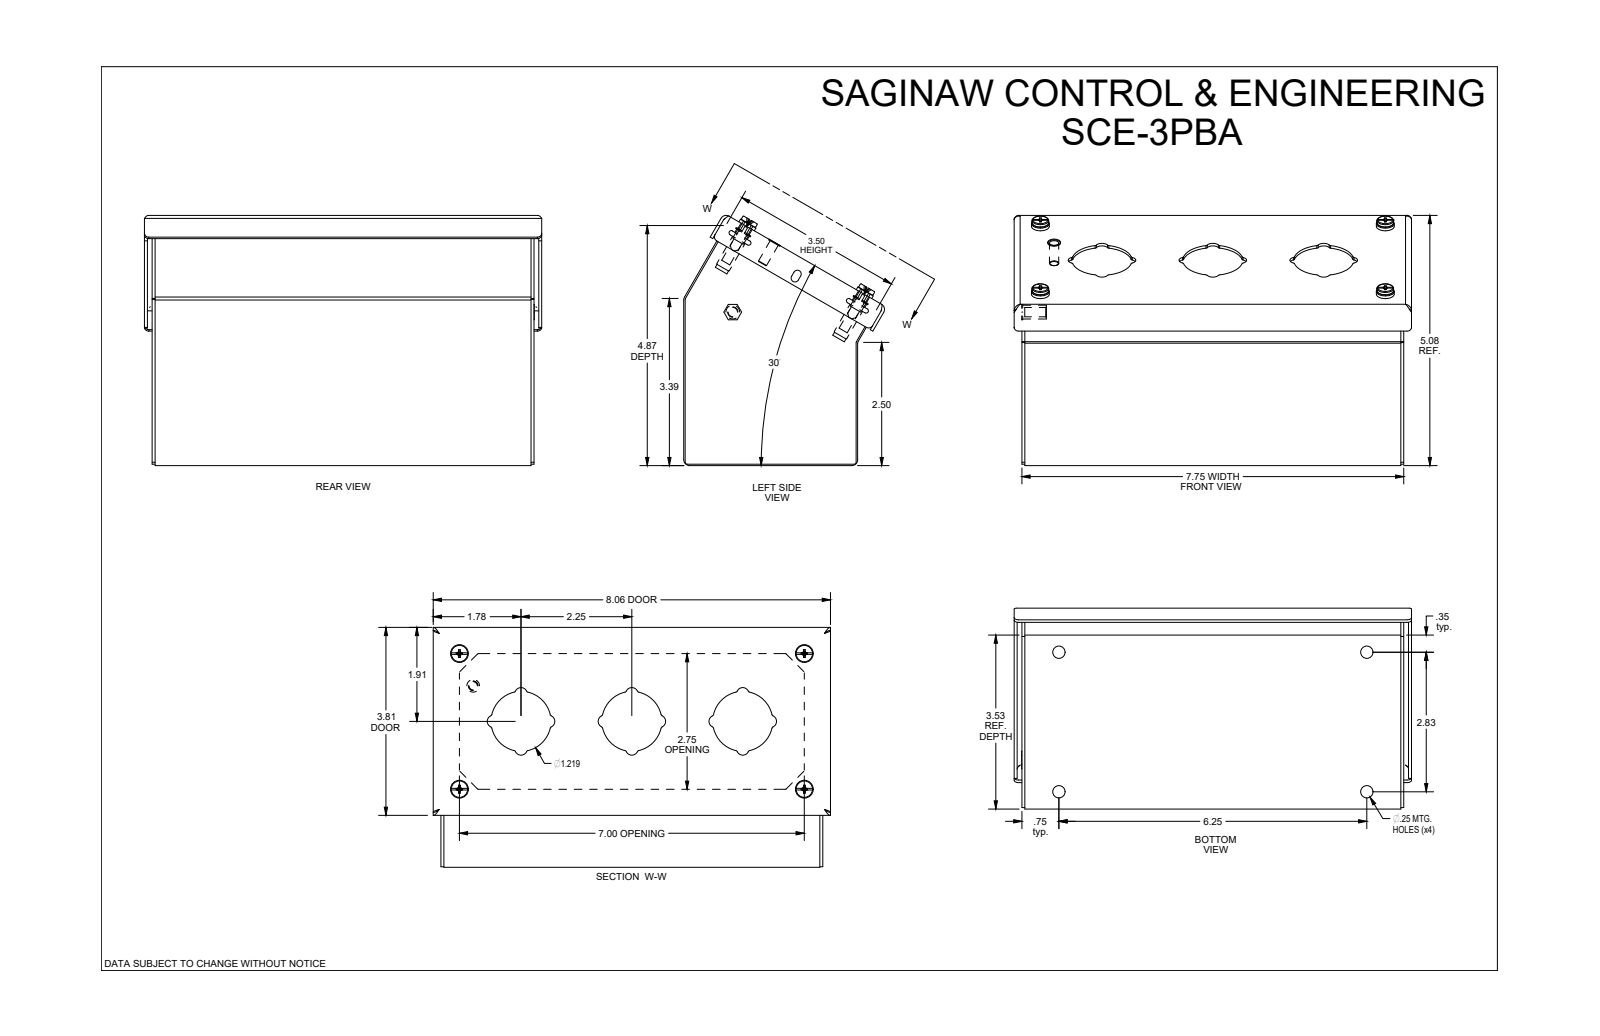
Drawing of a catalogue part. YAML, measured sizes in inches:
part_name: "SCE-3PBA"
step_written_by: "SolidWorks 2021 (AUTOMOTIVE_DESIGN)"
units: inches
bodies: {solids: 16, faces: 442, planar: 164, cylindrical: 136, other: 142}
overall_size: [8.062, 5.098, 4.097]
volume: 10.13
surface_area: 343
round_holes:
  - {diameter: 0.19, count: 5}
  - {diameter: 0.22, count: 4}
  - {diameter: 0.25, count: 4}
  - {diameter: 0.266, count: 4}
  - {diameter: 0.317, count: 4}
round_bosses_or_shafts:
  - {diameter: 0.188, count: 5}
  - {diameter: 0.362, count: 4}
  - {diameter: 0.34, count: 4}
  - {diameter: 0.334, count: 4}
  - {diameter: 0.292, count: 4}
  - {diameter: 0.27, count: 4}
  - {diameter: 0.26, count: 4}
  - {diameter: 0.146, count: 4}
partial_cylinders:
  - {radius: 0.04, count: 24}
  - {radius: 0.06, count: 22}
  - {radius: 0.125, count: 12}
  - {radius: 0.12, count: 6}
  - {radius: 0.609, count: 3}
face_to_face_distances: [0.06, 0.06, 3.47, 7.69, 3.53, 3.41, 7.75, 7.63, 0.156, 3.599]
hole_center_spacings: [2.753, 7, 2.75, 7.522, 6.995, 7.005, 7.517, 7.521]
